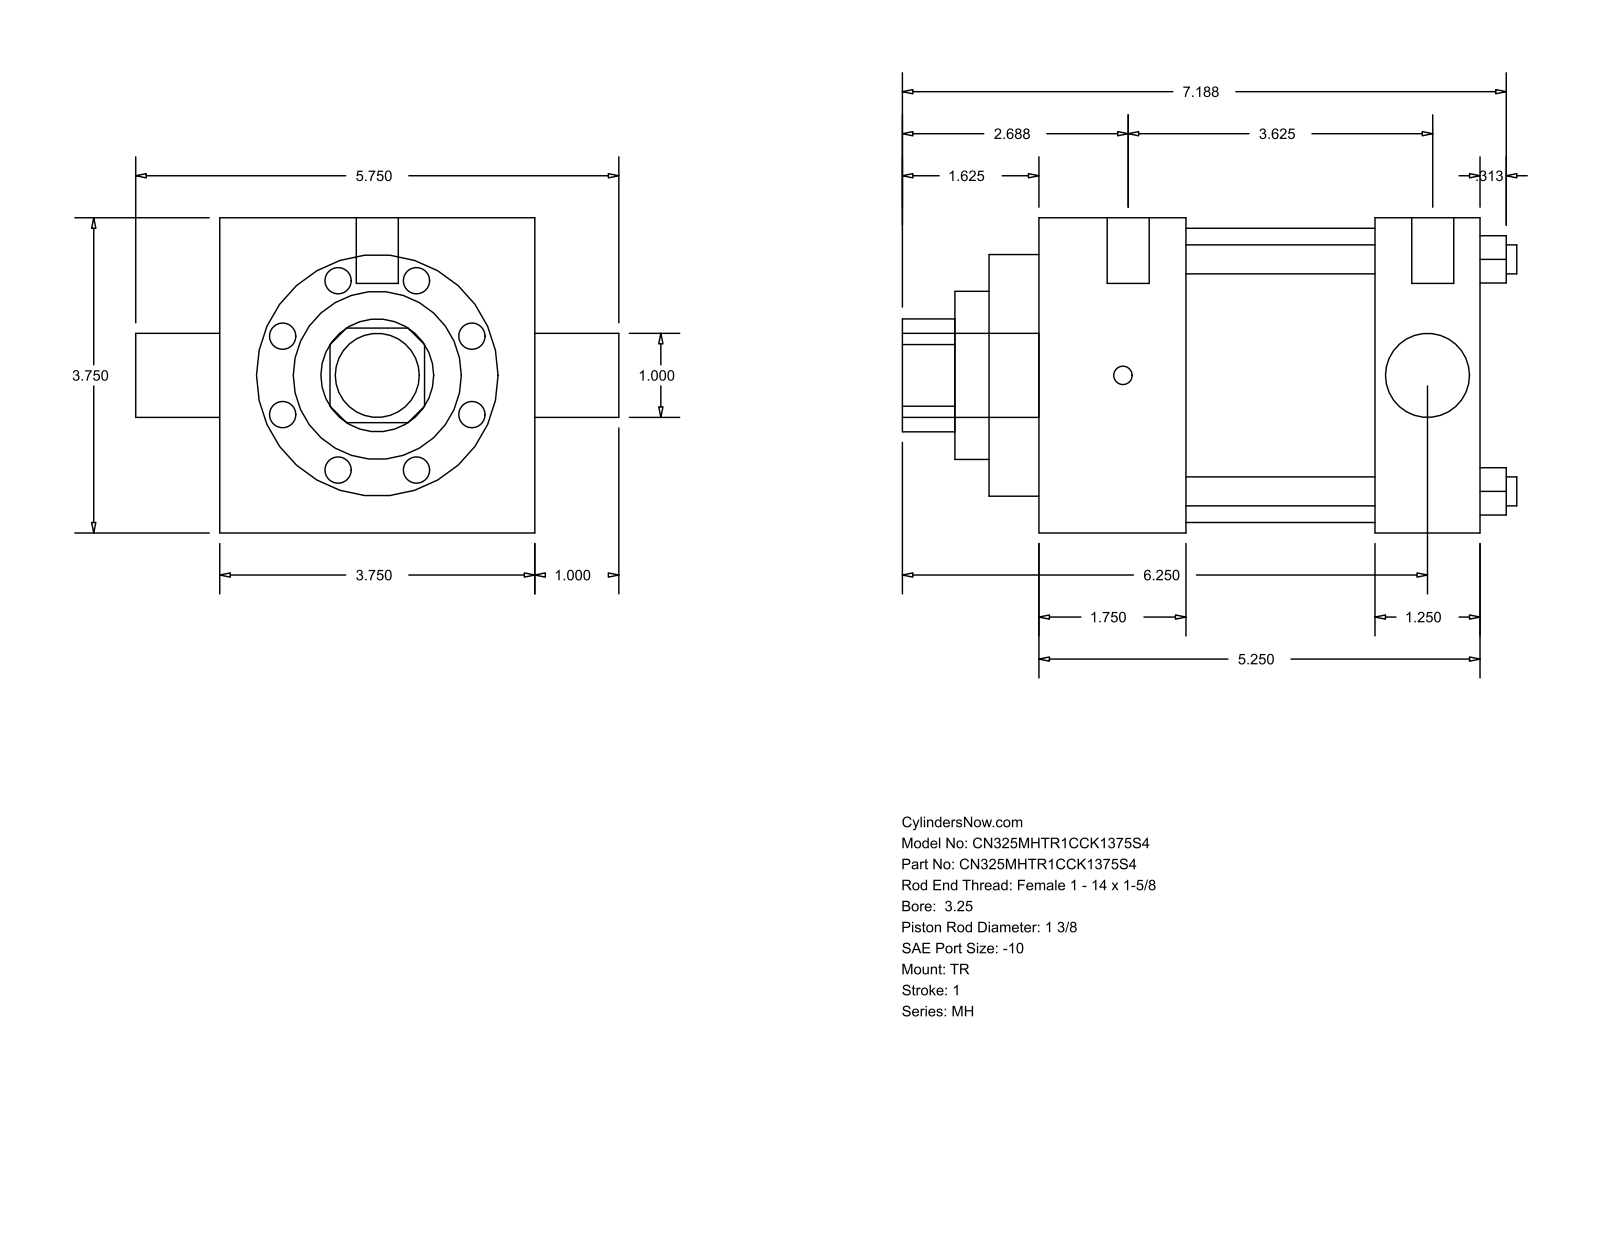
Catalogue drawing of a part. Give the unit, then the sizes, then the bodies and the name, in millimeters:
Units: millimetres
Overall size (bounding box): 185.74 × 146.05 × 95.25
Round holes (diameter × count): ⌀8.76 ×4, ⌀25.4 ×1, ⌀34.92 ×1, ⌀50.8 ×1, ⌀73.03 ×1, ⌀88.9 ×1
Round bosses / shafts (diameter × count): ⌀5.56 ×3, ⌀12.7 ×2, ⌀25.4 ×1
Partial cylindrical surfaces — rounded edges, fillets, slot ends (radius × count): R17.06 ×1
Main face-to-face distances: 95.24, 133.35, 44.45, 101.61, 57.16, 88.9, 31.74, 15.08, 59.53, 116.69
Hole centre spacings: 49.57, 70.1, 99.14
Bodies: 0 solids, 86 faces (61 planar, 25 cylindrical, 0 other)
Part name (STEP PRODUCT): MH_TR__0325_1.375
STEP written by: GSSL Pune (CONFIG_CONTROL_DESIGN)
